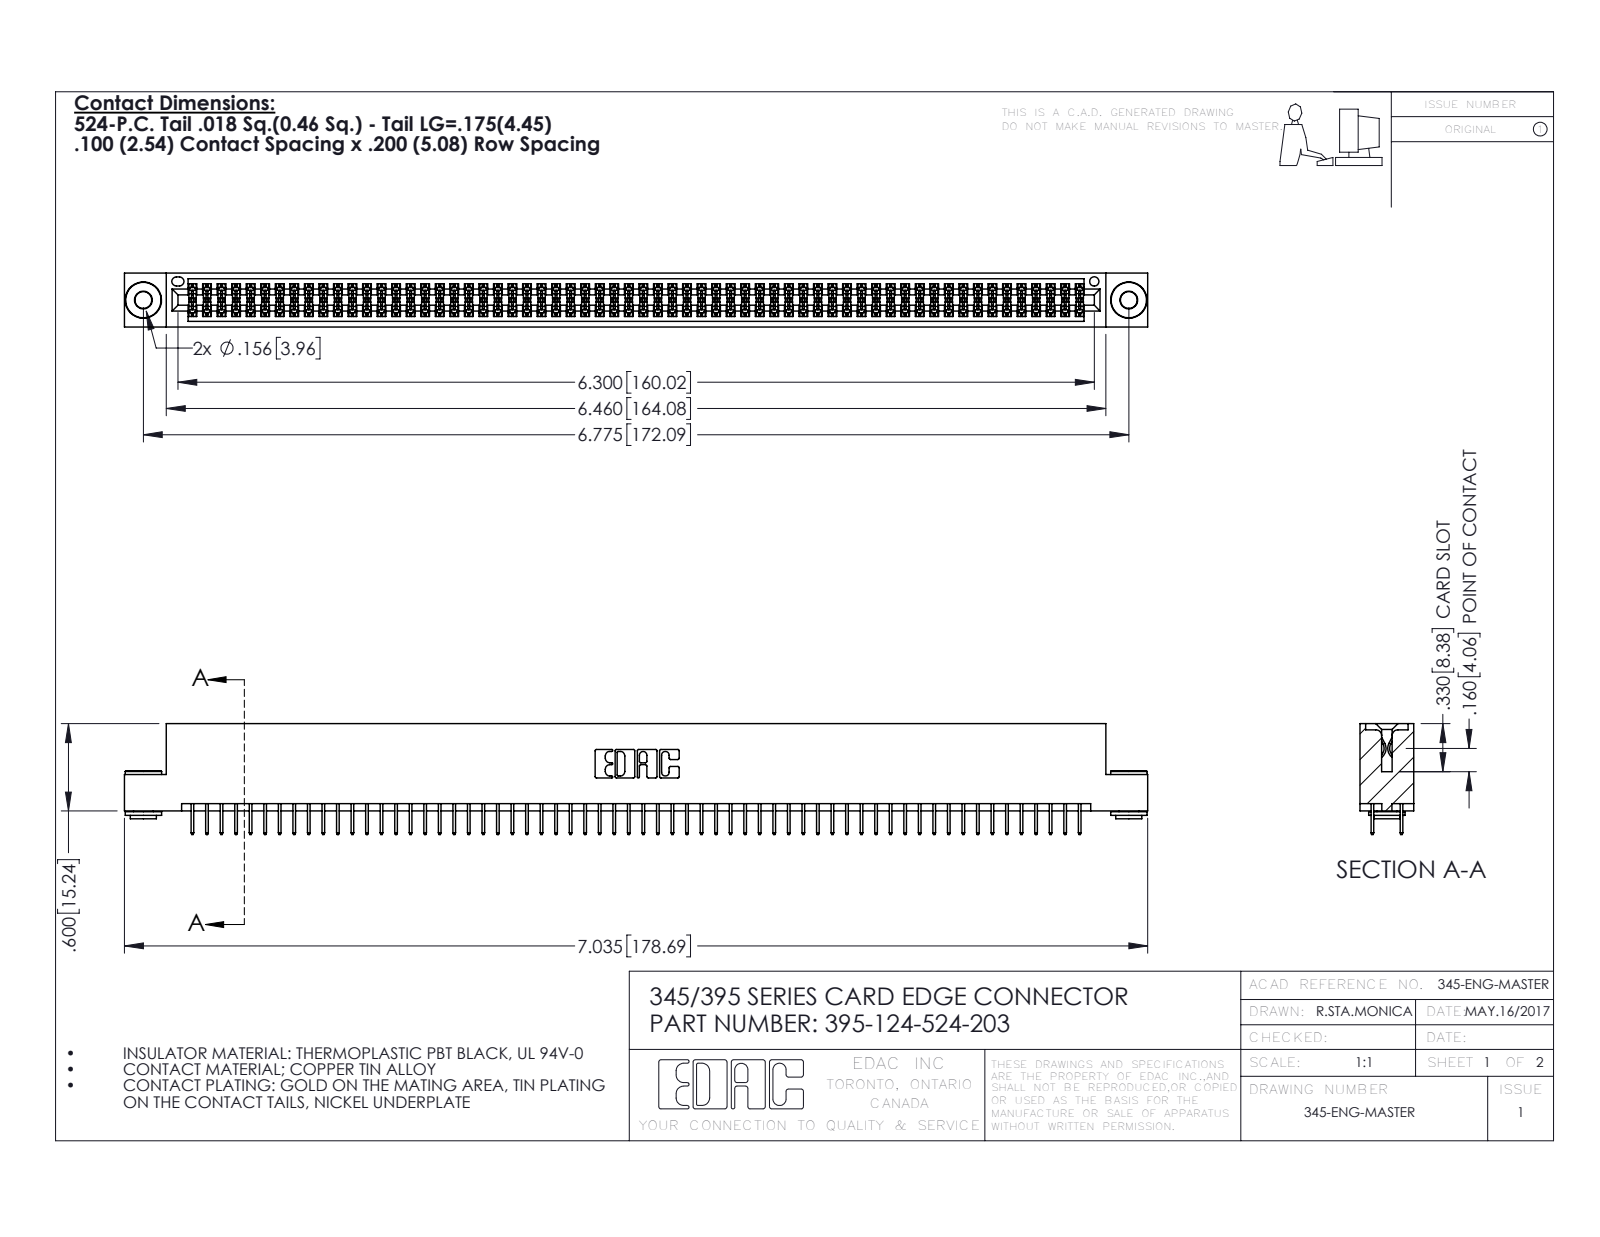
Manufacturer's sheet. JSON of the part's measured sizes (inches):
{"part_name": "345 Part_Flush Mounting Lugs - 0.156 Dia-TH; 345-292-001_345-293-124; 345-250-002_345-250-002-102; 395-124-524-203", "step_written_by": "SolidWorks 2016 (CONFIG_CONTROL_DESIGN)", "units": "inches", "bodies": {"solids": 127, "faces": 6860, "planar": 4926, "cylindrical": 1926, "other": 8}, "overall_size": [7.035, 0.762, 0.37], "volume_in3": 1.06, "surface_area_in2": 39.96, "round_holes": [[0.116, 2], [0.156, 2], [0.064, 1]], "round_bosses_or_shafts": [[0.25, 2], [0.18, 2], [0.136, 2]], "partial_cylinders_radius": [[0.006, 186], [0.01, 22], [0.007, 6], [0.031, 6], [0.026, 3], [0.014, 2], [0.019, 2], [0.022, 2]], "face_to_face_distances": [0.072, 0.298, 0.2, 0.37, 0.025, 0.098, 0.272, 0.225, 0.072, 0.175], "hole_center_spacings": [0.27, 6.539, 6.775]}
